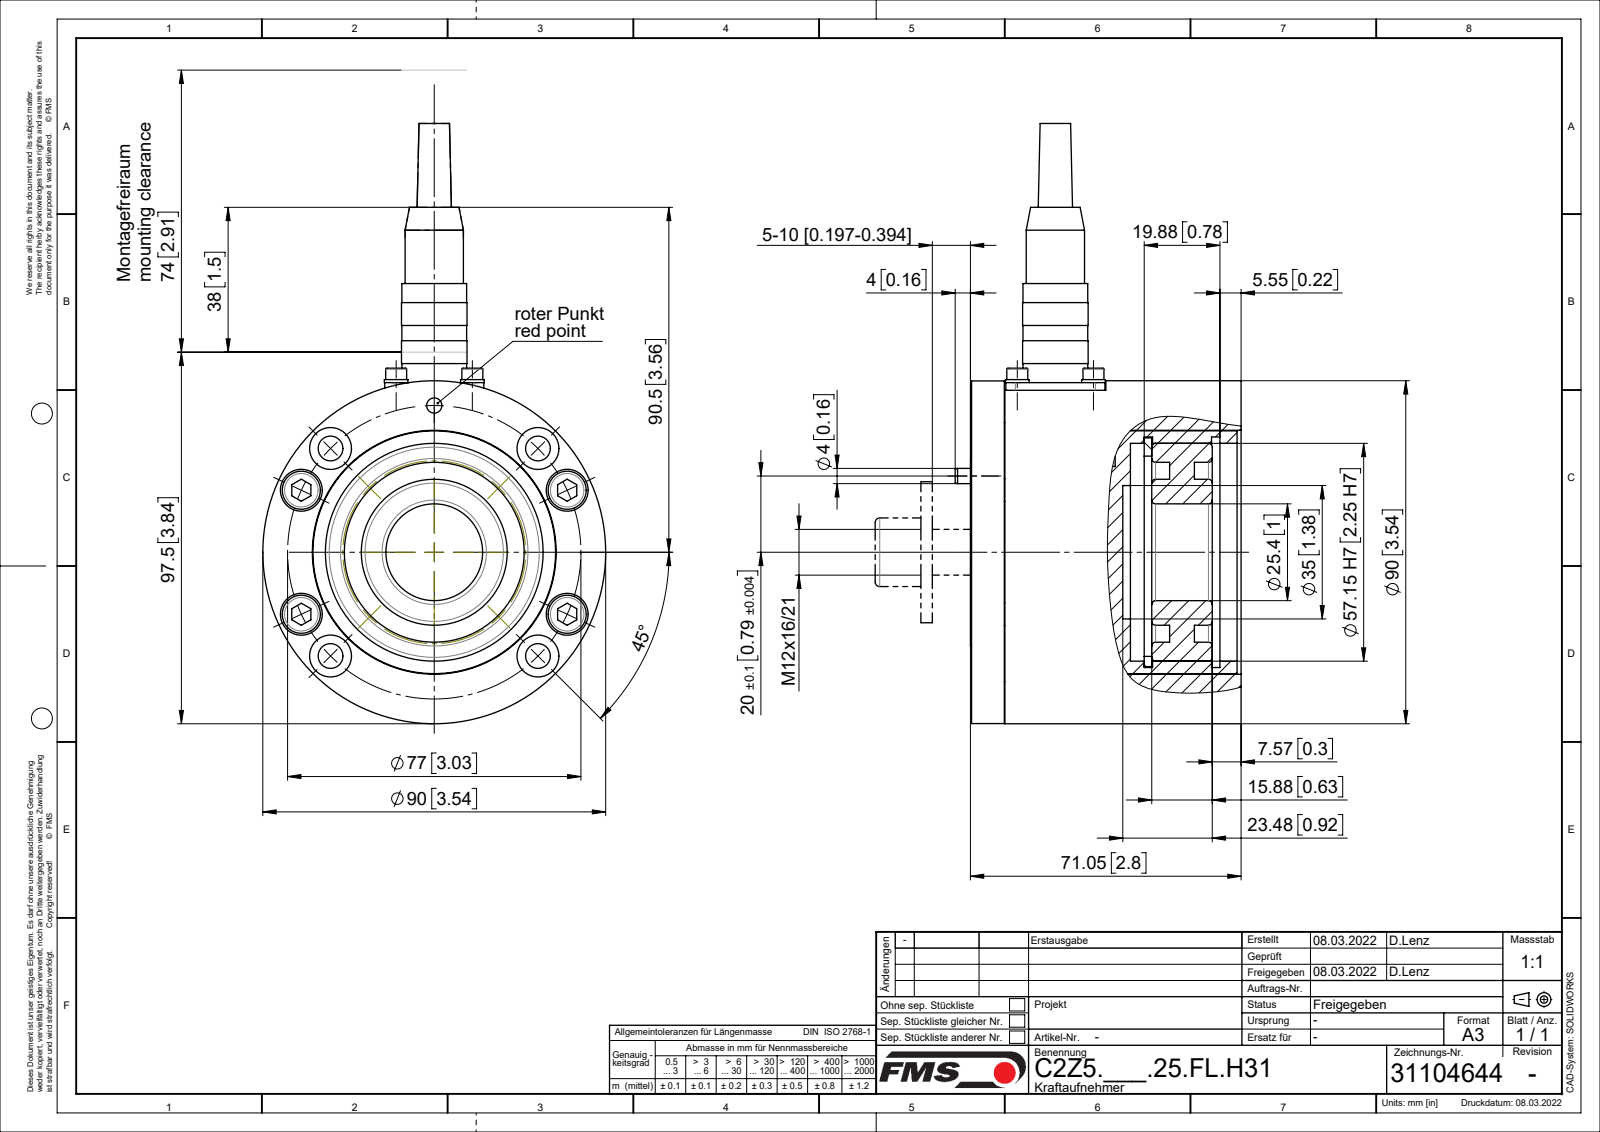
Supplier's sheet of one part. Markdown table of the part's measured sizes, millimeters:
| quantity | value |
| --- | --- |
| part name | Flanschstecker_M14x1_Mini_5pol; Zyl-Schr DIN912_M3x6; Si-Ring DIN472_D57.15; Federringe_DIN127A_M03 (+8 more) |
| STEP written by | SolidWorks 2018 (CONFIG_CONTROL_DESIGN) |
| units | millimeters |
| bodies | 22 solids, 547 faces (185 planar, 254 cylindrical, 108 other) |
| overall size | 157.5 × 96.05 × 90 |
| volume | 316 332 mm³ |
| surface area | 122 946 mm² |
| round holes (diameter × count) | 6.5 × 8, 11 × 8, 2.5 × 6, 3.1 × 4, 3.2 × 4, 5 × 4, 7 × 4, 4 × 2, 3 × 1, 10.2 × 1, 12 × 1, 13 × 1 |
| round bosses / shafts (diameter × count) | 1.5 × 5, 10 × 4, 6.2 × 4, 6 × 4, 5.5 × 4, 3 × 4, 90 × 1, 89.9 × 1 |
| partial cylindrical surfaces (radius × count) | 0.1 × 4, 2.5 × 4, 0.5 × 2, 4.16 × 2, 5 × 2, 23.2 × 1, 26.29 × 1 |
| main face-to-face distances | 6, 33.05, 32, 2, 38, 8.6, 29.1, 37.7, 2.9, 5.7 |
| hole center spacings | 20, 38.5, 13.37, 14.14, 38.49, 44.16, 54.44, 63.07 |
